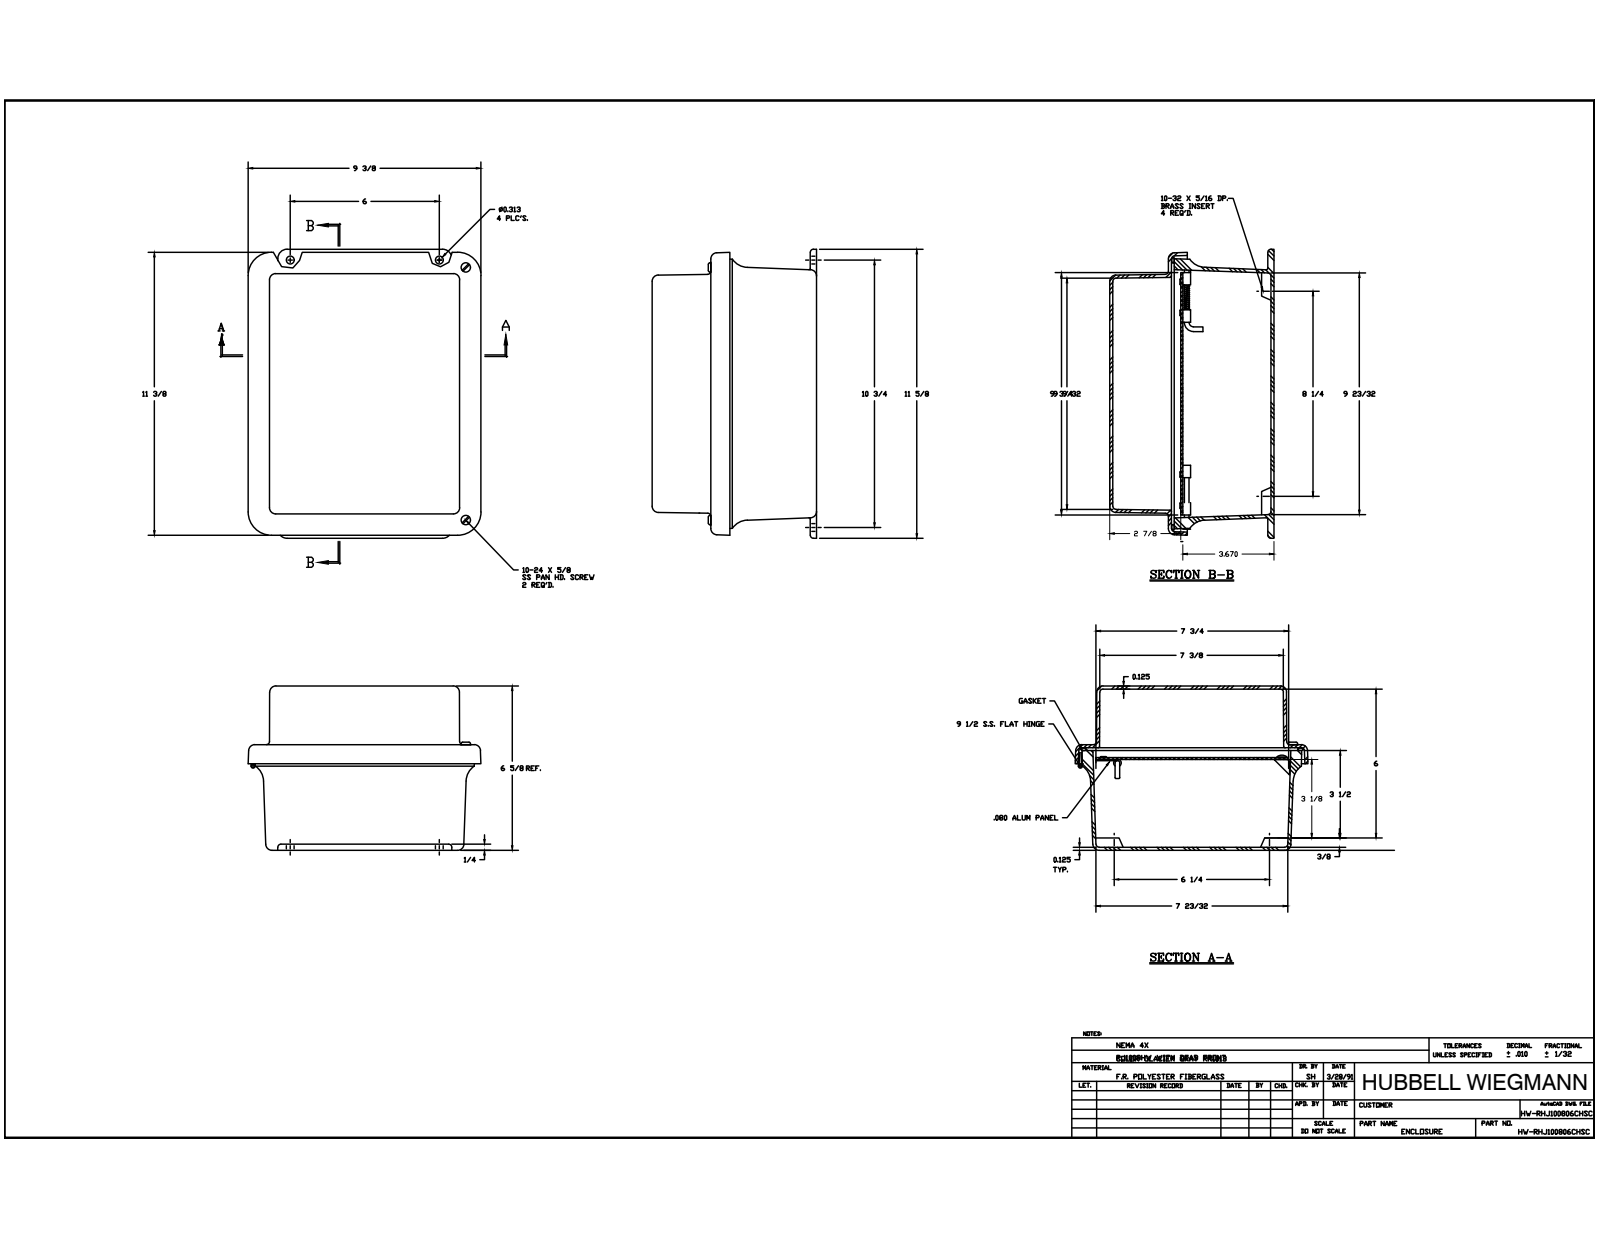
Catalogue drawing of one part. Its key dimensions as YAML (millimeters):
part_name: "J1008HW_5; RMINS45821P_133; RMINS45821P_134; RMINS45821P_135 (+8 more)"
step_written_by: "Autodesk Inventor 2014 (AUTOMOTIVE_DESIGN)"
units: millimeters
bodies: {solids: 22, faces: 801, planar: 269, cylindrical: 303, other: 229}
overall_size: [295.27, 238.59, 167.48]
volume: 1121000
surface_area: 615823
round_holes:
  - {diameter: 3.33, count: 8}
  - {diameter: 3.56, count: 8}
  - {diameter: 3.86, count: 5}
  - {diameter: 3.96, count: 4}
  - {diameter: 5.54, count: 4}
  - {diameter: 3.68, count: 2}
  - {diameter: 2.16, count: 1}
  - {diameter: 2.16, count: 1}
round_bosses_or_shafts:
  - {diameter: 6.35, count: 8}
  - {diameter: 3.17, count: 8}
  - {diameter: 6.86, count: 6}
  - {diameter: 4.83, count: 2}
  - {diameter: 3.97, count: 2}
  - {diameter: 3.94, count: 1}
partial_cylinders:
  - {radius: 3.17, count: 24}
  - {radius: 0.79, count: 20}
  - {radius: 6.35, count: 12}
  - {radius: 5.08, count: 4}
  - {radius: 9.53, count: 4}
  - {radius: 19.05, count: 4}
  - {radius: 1.6, count: 2}
face_to_face_distances: [3.17, 3.18, 161.13, 164.3, 167.48, 164.31, 104.36, 101.19, 59.94, 63.12]
hole_center_spacings: [152.4, 76.2, 6.35, 33.96, 63.5, 69.85, 184.17, 234.96]
